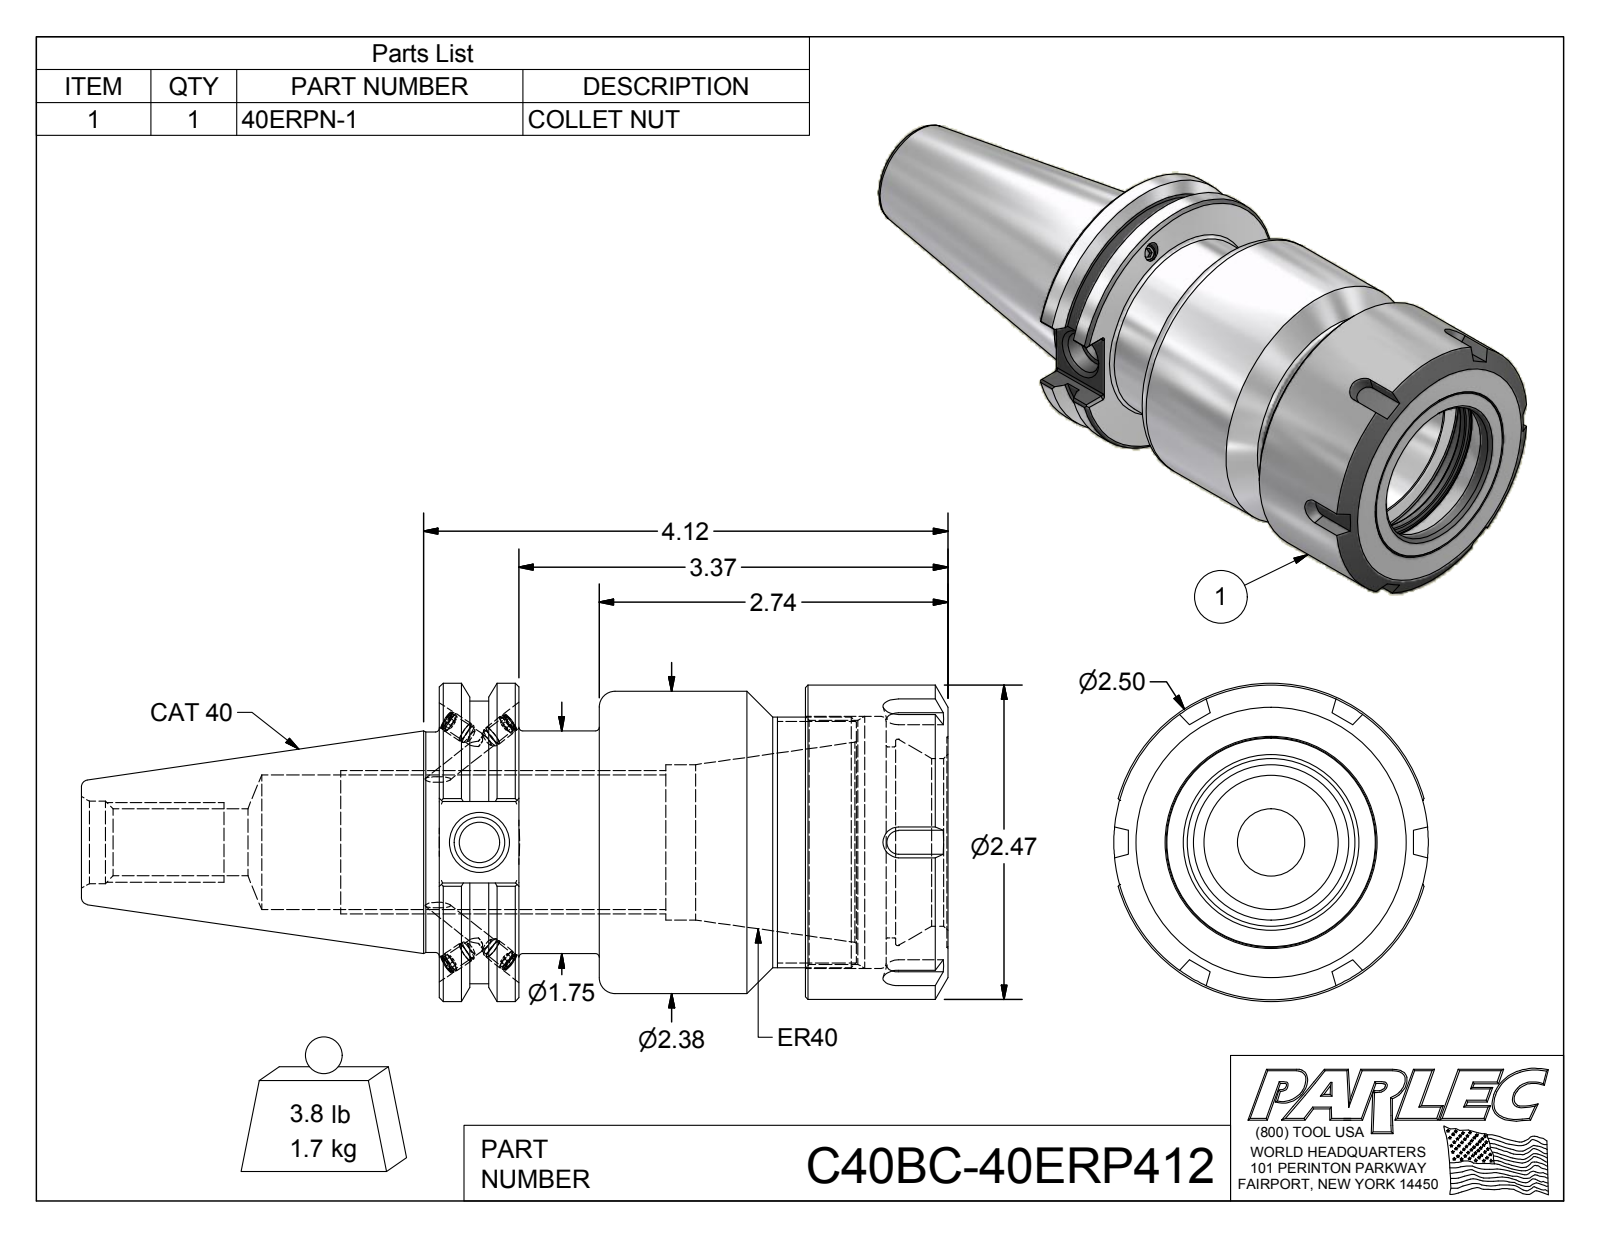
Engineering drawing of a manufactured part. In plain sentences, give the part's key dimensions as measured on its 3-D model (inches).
The part is named "C40BC-40ERP412; C40BCB-40ER4-1; 029-965; 40ERPN". Its 3-D file was written by "Autodesk Inventor 2012 (AUTOMOTIVE_DESIGN)". It is 6 solids with 213 faces: 100 planar, 54 cylindrical and 59 other. Overall it measures 6.808 by 2.5 by 2.47 inches. Its volume is 13.47 cubic inches and its surface area 87.06 square inches. Round holes: 4 of diameter 0.13, 4 of diameter 0.161, 1 of diameter 0.315, 1 of diameter 0.399, 1 of diameter 0.527, 1 of diameter 0.648, 1 of diameter 1.057, 1 of diameter 1.22, 1 of diameter 1.318, 1 of diameter 1.5, 1 of diameter 1.62, 1 of diameter 1.916. Round bosses or shafts: 4 of diameter 0.165, 4 of diameter 0.157, 1 of diameter 2.5, 1 of diameter 2.47, 1 of diameter 2.375, 1 of diameter 2.219, 1 of diameter 1.969, 1 of diameter 1.75. Partial cylindrical surfaces (rounded edges, fillets, slot ends): 12 of radius 0.02. The main face-to-face distances are 3.995, 0.625, 3.37, 2.875, 2.25, 1.12, 3.511, 2.886, 0.636, 0.484.
